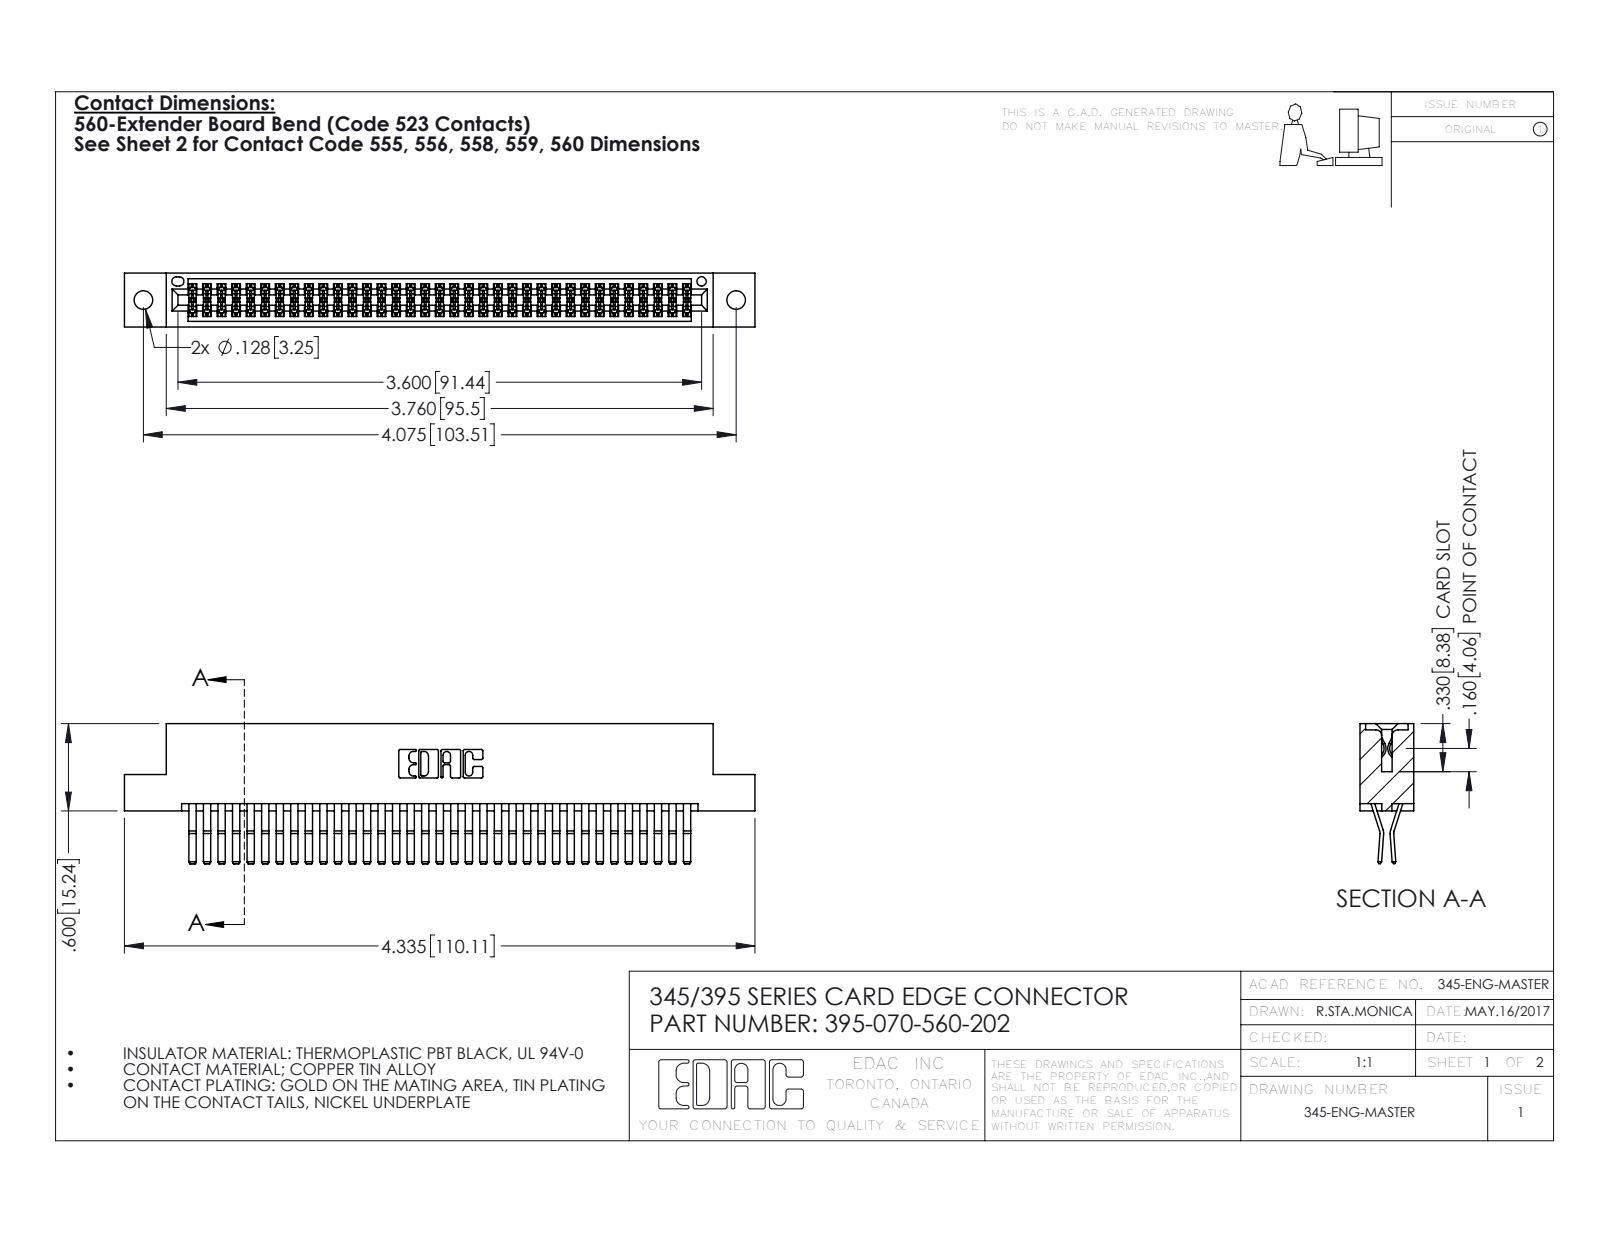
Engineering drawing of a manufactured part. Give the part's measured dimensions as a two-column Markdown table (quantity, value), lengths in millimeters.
| quantity | value |
| --- | --- |
| part name | 345-292-001_560 Tail; 395-070-560-202; 345 Part_Flush Mounting Lugs - 0.128 Dia |
| STEP written by | SolidWorks 2016 (CONFIG_CONTROL_DESIGN) |
| units | millimeters |
| bodies | 71 solids, 3766 faces (2390 planar, 1376 cylindrical, 0 other) |
| overall size | 110.1 × 24.4 × 9.4 |
| volume | 11 100 mm³ |
| surface area | 17 110 mm² |
| round holes (diameter × count) | 3.3 × 2, 1.6 × 1 |
| partial cylindrical surfaces (radius × count) | 0.2 × 105, 0.3 × 22, 0.2 × 6, 0.8 × 6, 0.7 × 3, 0.3 × 2, 0.4 × 2, 0.5 × 2 |
| main face-to-face distances | 0.6, 7.6, 1.8, 9.4, 5.1, 2.5, 6.9, 5.7, 4.4, 3.8 |
| hole center spacings | 6.9, 97.5, 103.5 |
